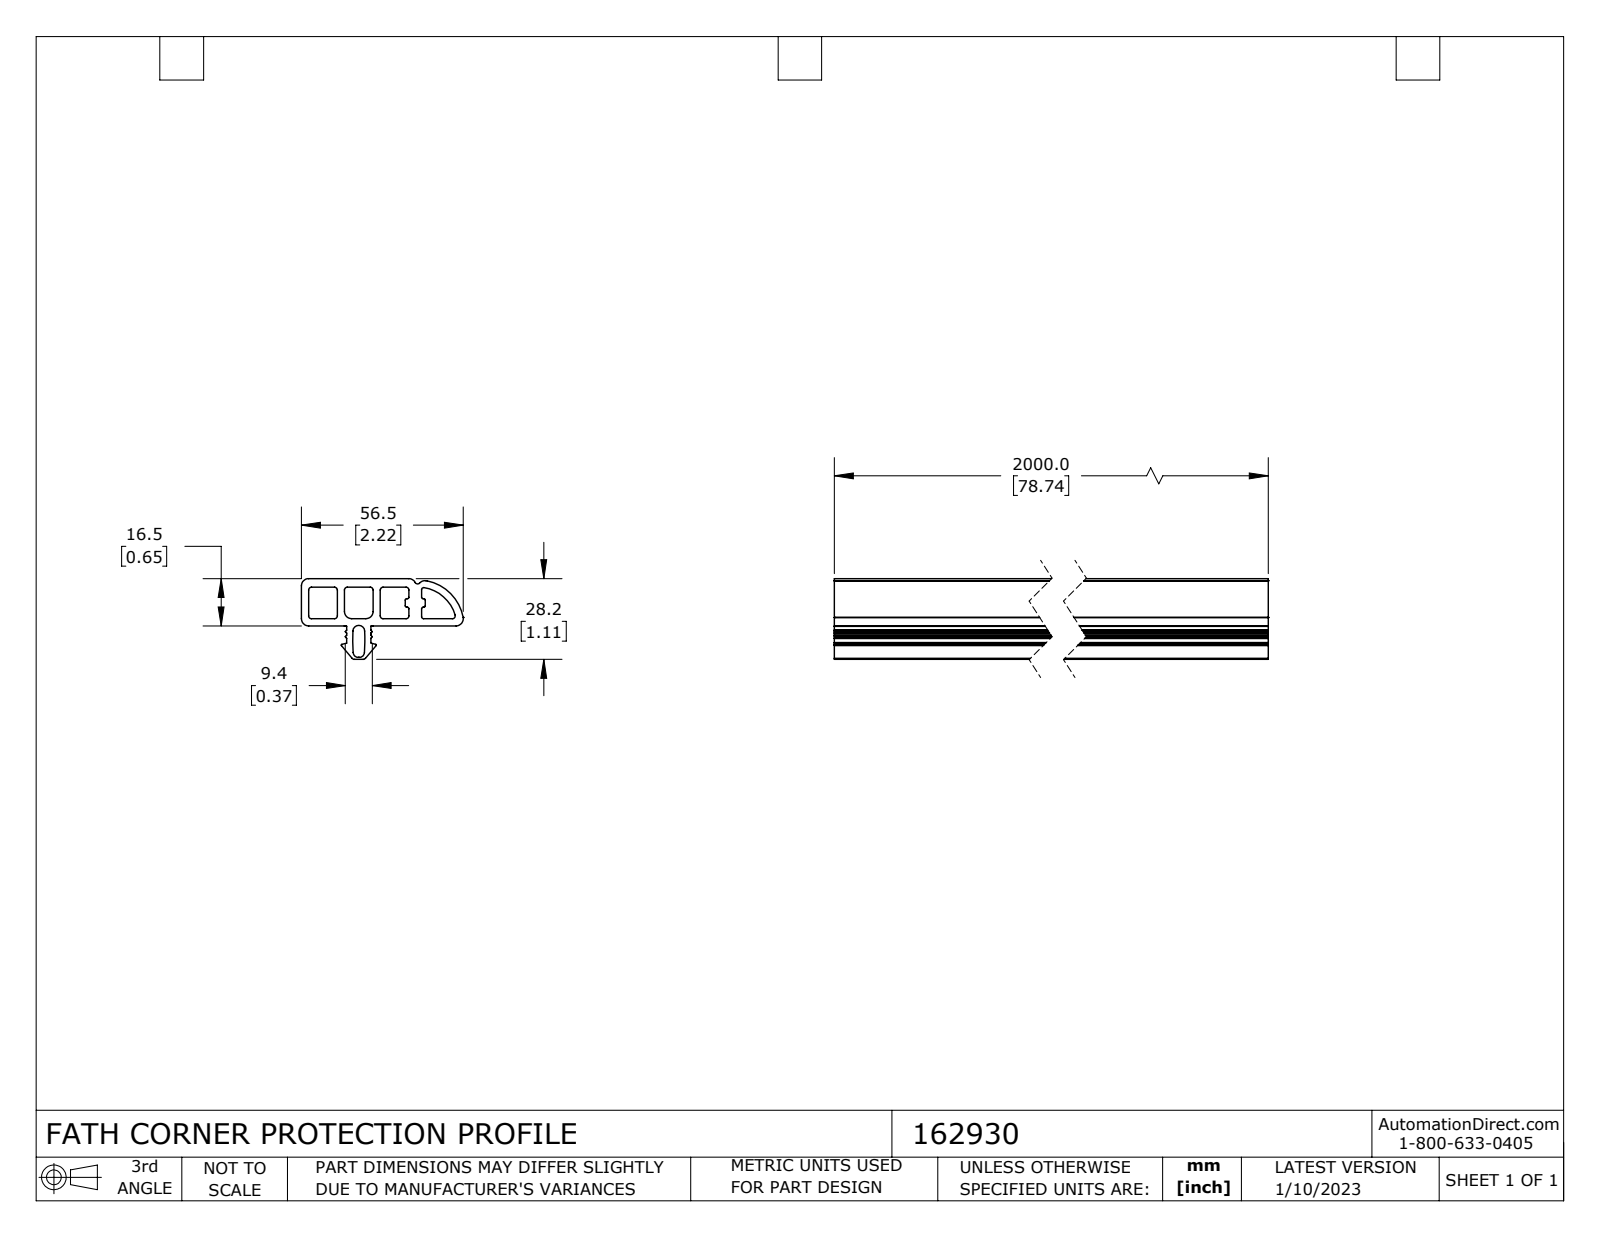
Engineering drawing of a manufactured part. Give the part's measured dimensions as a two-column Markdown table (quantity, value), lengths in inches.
| quantity | value |
| --- | --- |
| part name | 162930 |
| STEP written by | SolidWorks 2021 (CONFIG_CONTROL_DESIGN) |
| units | inches |
| bodies | 1 solid, 110 faces (52 planar, 56 cylindrical, 2 other) |
| overall size | 78.74 × 2.224 × 1.11 |
| volume | 62.18 in³ |
| surface area | 1 090 in² |
| partial cylindrical surfaces (radius × count) | 0.008 × 15, 0.039 × 15, 0.02 × 8, 0.098 × 5, 0.028 × 2, 0.071 × 2, 0.098 × 2, 0.035 × 1 |
| main face-to-face distances | 0.098, 0.65, 0.551, 0.492, 0.118, 0.433, 0.531, 0.394, 0.984, 0.886 |
